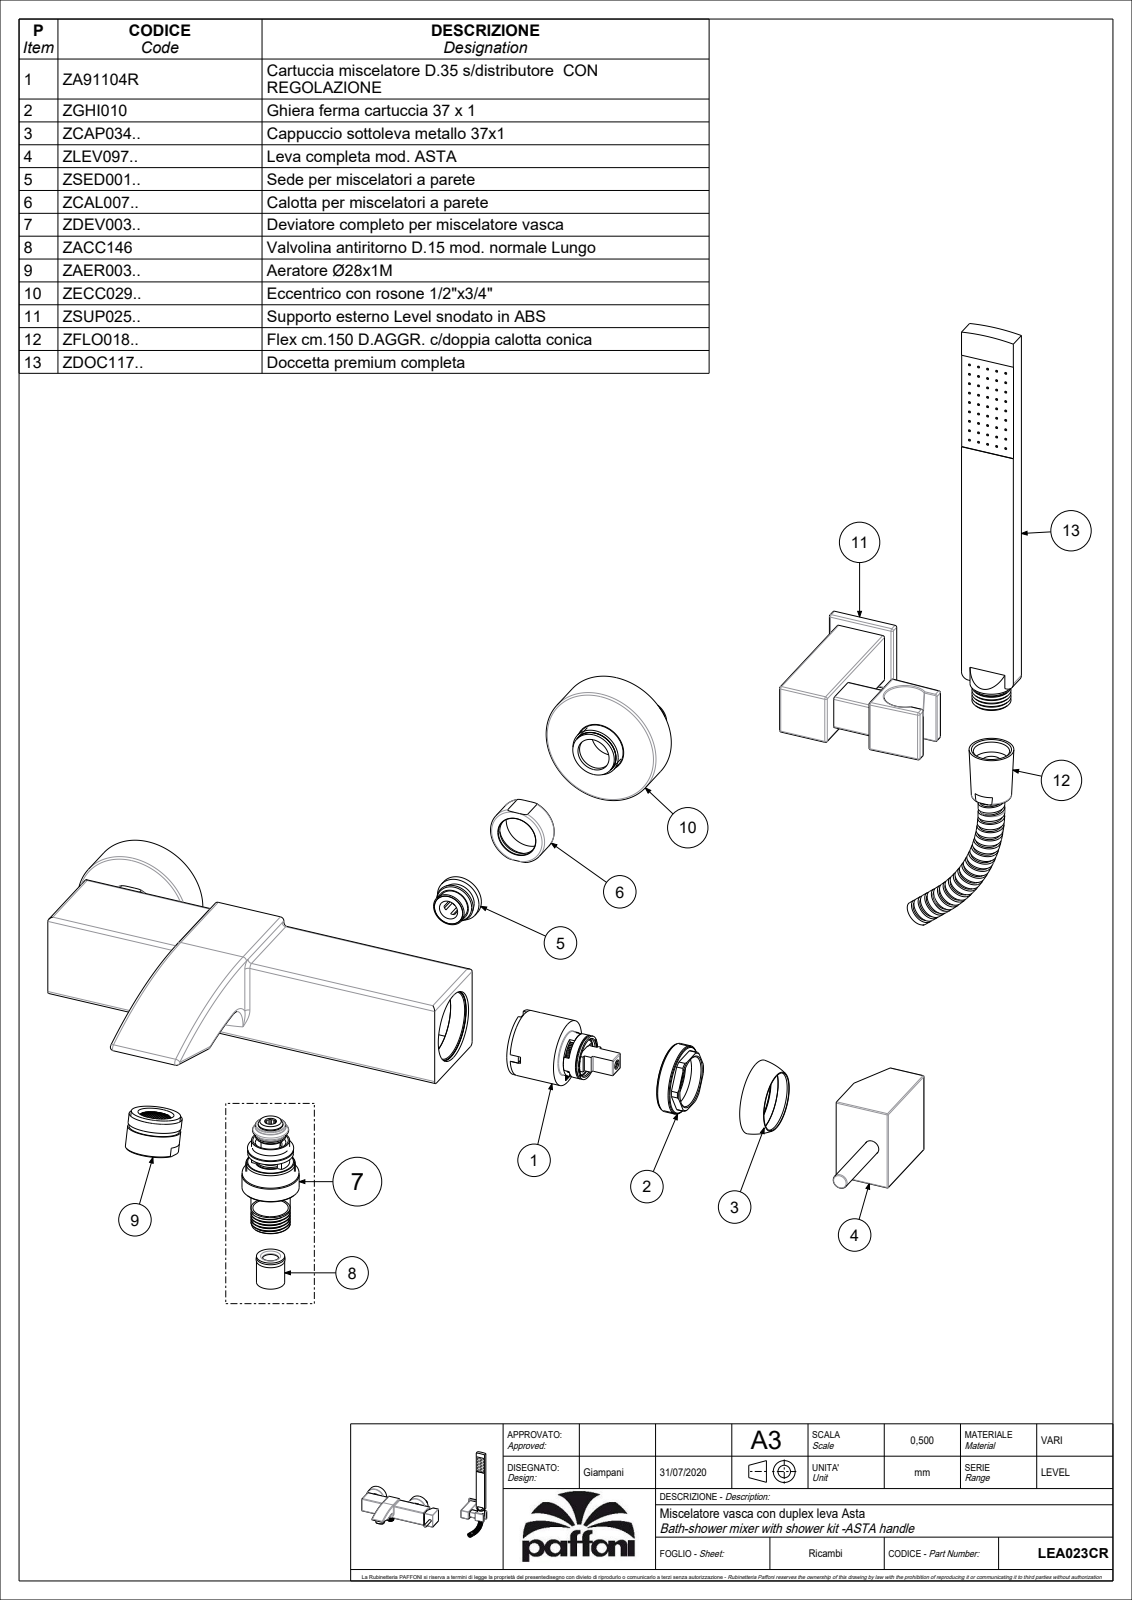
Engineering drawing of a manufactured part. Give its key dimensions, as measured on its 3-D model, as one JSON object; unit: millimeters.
{"part_name": "LEA023CR", "step_written_by": "CREO PARAMETRIC BY PTC INC, 2020044 (CONFIG_CONTROL_DESIGN)", "units": "millimeters", "bodies": {"solids": 3, "faces": 3349, "planar": 2537, "cylindrical": 460, "other": 352}, "overall_size": [447.5, 330.5, 166.24], "volume_mm3": 498379, "surface_area_mm2": 254075, "round_holes": [[7, 4], [24.5, 3], [25, 3], [4, 2], [10.5, 2], [16.5, 2], [18, 2], [21, 2], [21.6, 2], [28.5, 2], [31, 2], [37, 2]], "round_bosses_or_shafts": [[2, 11], [27, 3], [24, 3], [63.5, 2], [28, 2], [37, 1], [35.5, 1], [35, 1]], "partial_cylinders_radius": [[0.5, 43], [1, 34], [2, 15], [0.15, 11], [0.3, 4], [4, 2], [15.6, 2], [3, 1]], "face_to_face_distances": [3.75, 42.75, 46.5, 18.75, 39, 15, 24, 3, 25, 27.75], "hole_center_spacings": [7.07, 8.6, 11.4, 4, 6, 10, 14, 14.6]}
